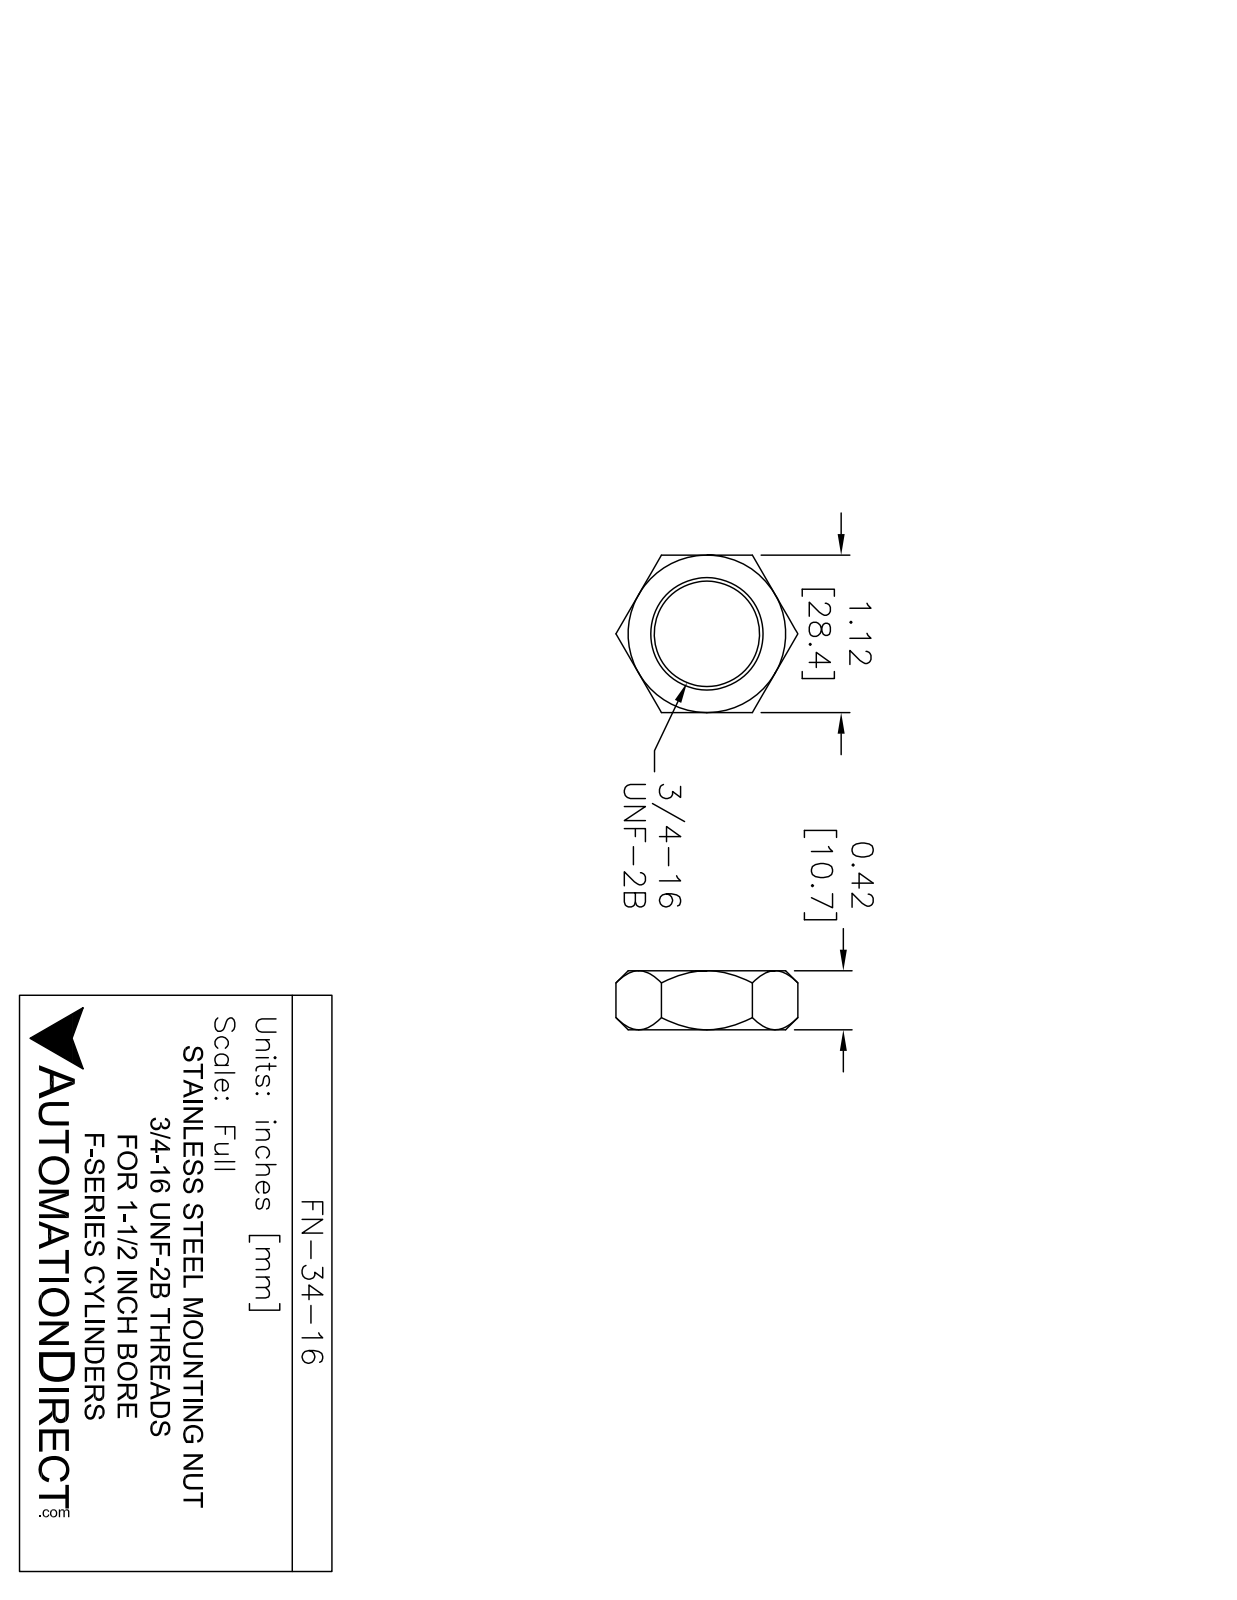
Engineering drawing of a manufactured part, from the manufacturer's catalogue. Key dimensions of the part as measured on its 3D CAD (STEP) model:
Part name (STEP PRODUCT): FN-34-16
STEP written by: SolidWorks 2017 (AUTOMOTIVE_DESIGN)
Units: inches
Bodies: 1 solid, 14 faces (8 planar, 2 cylindrical, 4 other)
Overall size (bounding box): 1.299 × 1.125 × 0.42
Volume: 0.299 in³ · Surface area: 3.833 in²
Round holes (diameter × count): ⌀0.687 ×1
Main face-to-face distances: 1.125, 0.42
